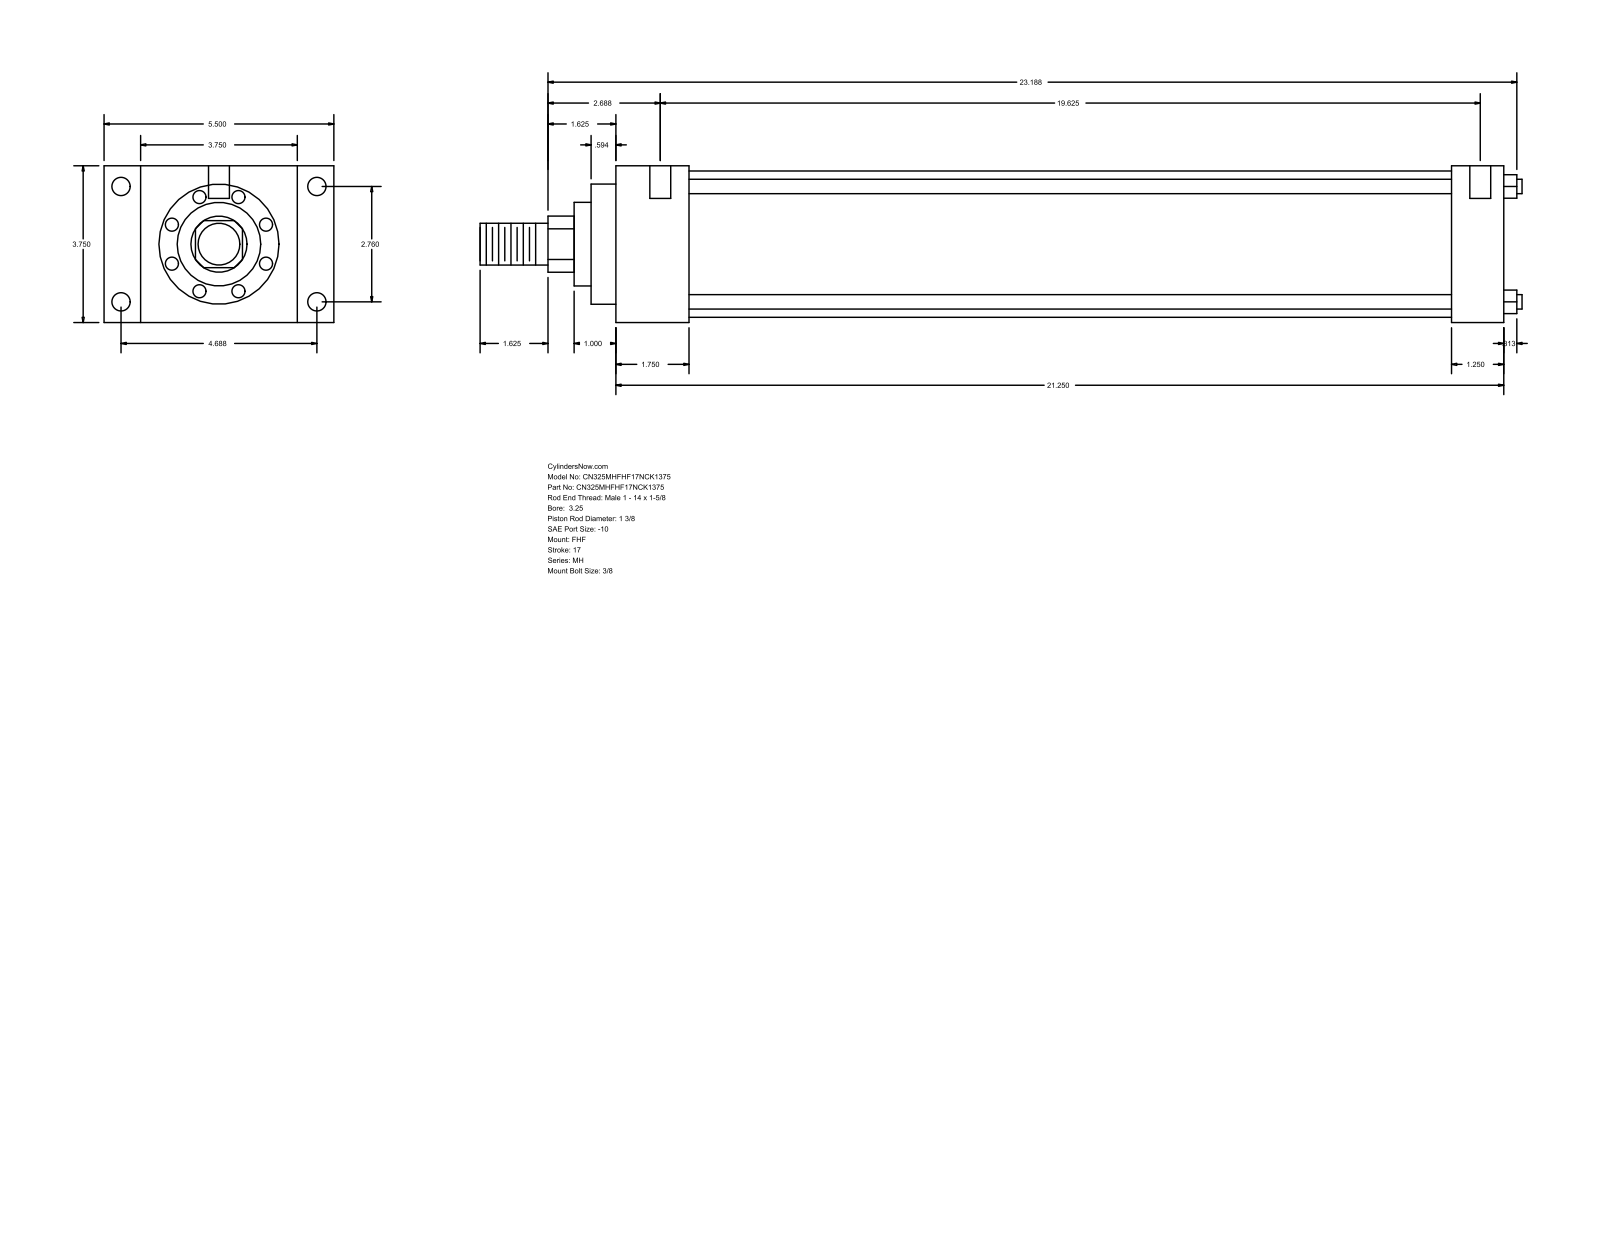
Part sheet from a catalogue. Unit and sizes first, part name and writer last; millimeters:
Units: millimetres
Overall size (bounding box): 633.41 × 139.7 × 95.25
Round holes (diameter × count): ⌀5.56 ×4, ⌀11.13 ×4, ⌀12.7 ×2
Round bosses / shafts (diameter × count): ⌀8.76 ×4, ⌀88.9 ×1, ⌀73.03 ×1, ⌀50.8 ×1, ⌀34.92 ×1, ⌀25.4 ×1
Partial cylindrical surfaces — rounded edges, fillets, slot ends (radius × count): R17.06 ×1
Main face-to-face distances: 95.24, 539.75, 44.45, 495.3, 22.23, 117.47, 139.7, 508, 463.55, 31.75
Hole centre spacings: 70.1, 119.06, 138.16, 504.83, 1.59, 4.76, 498.48, 500.07
Bodies: 0 solids, 90 faces (61 planar, 29 cylindrical, 0 other)
Part name (STEP PRODUCT): MH_FHF__0325_1.375
STEP written by: GSSL Pune (CONFIG_CONTROL_DESIGN)
